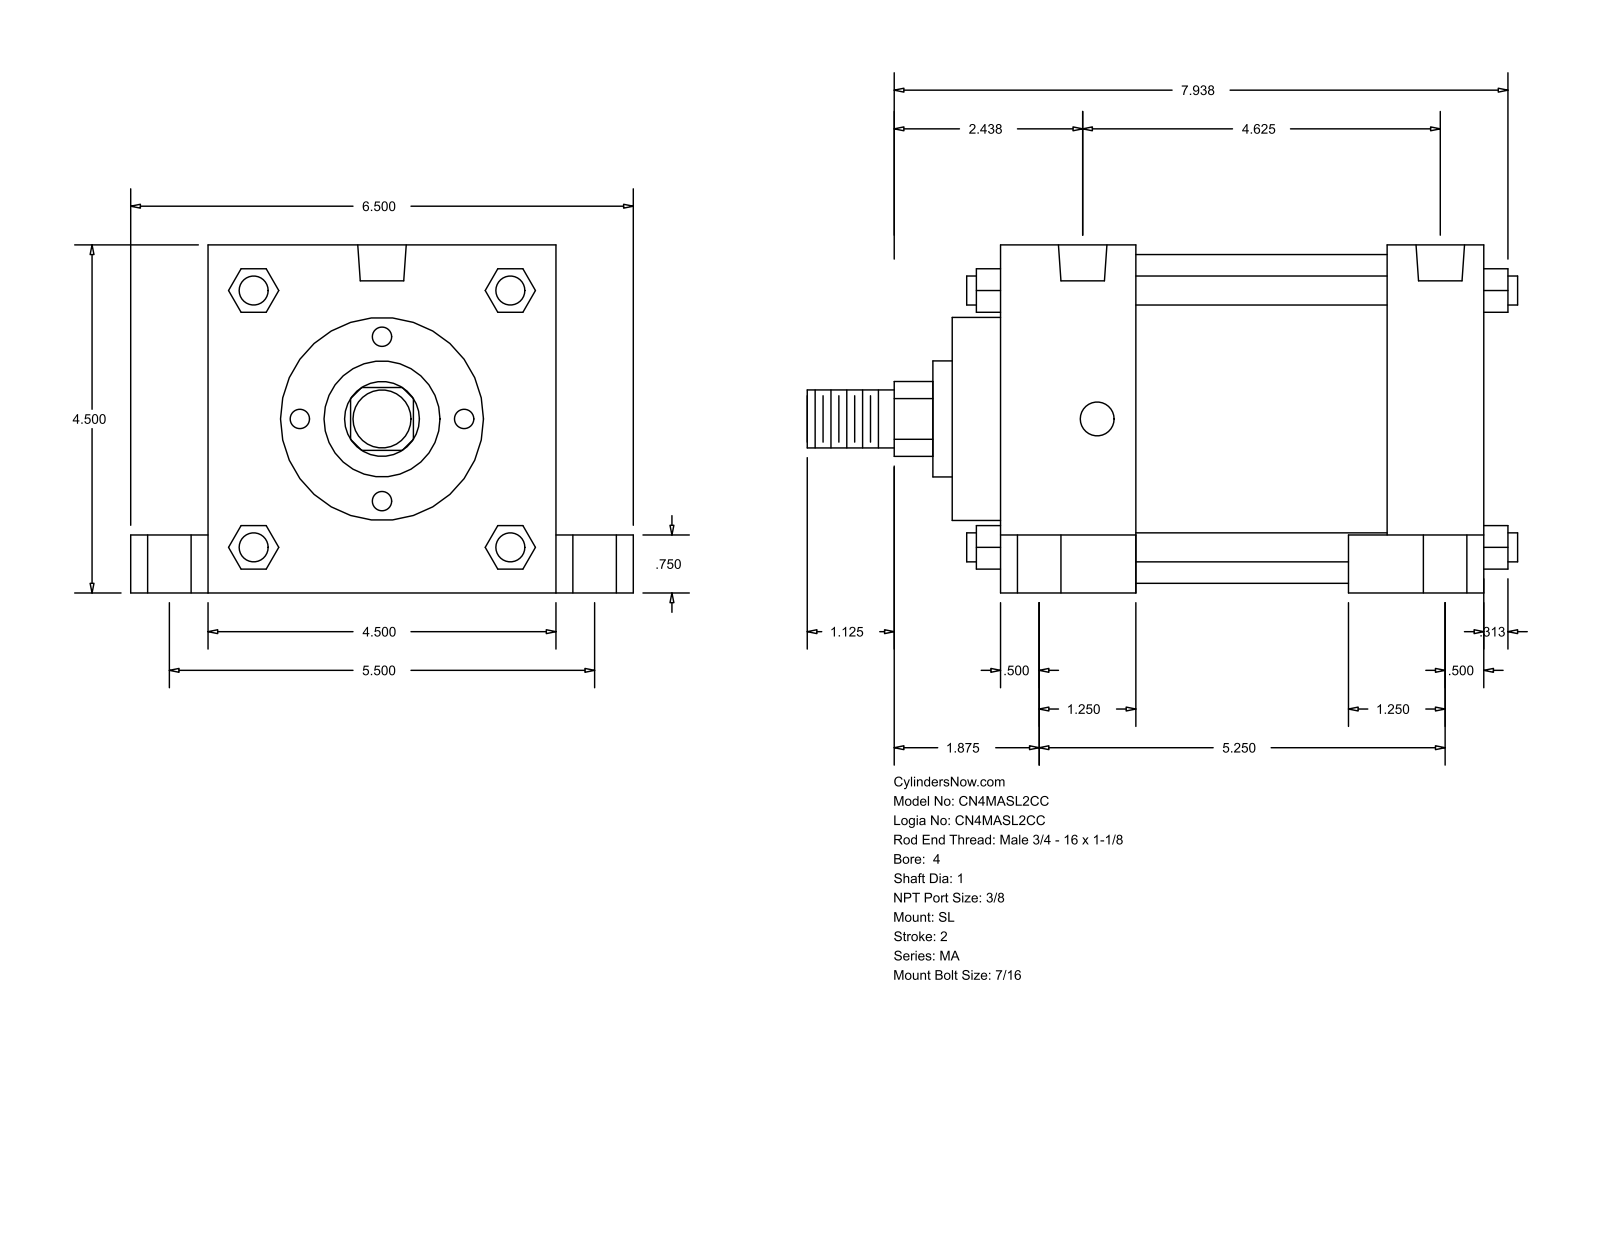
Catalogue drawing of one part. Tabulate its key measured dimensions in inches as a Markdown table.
| quantity | value |
| --- | --- |
| part name | MA_SL__0400_1 |
| STEP written by | GSSL Pune (CONFIG_CONTROL_DESIGN) |
| units | inches |
| bodies | 0 solids, 150 faces (113 planar, 37 cylindrical, 0 other) |
| overall size | 9.187 × 6.5 × 4.5 |
| round holes (diameter × count) | 0.437 × 4, 0.563 × 4, 0.813 × 4, 0.627 × 2 |
| round bosses / shafts (diameter × count) | 0.375 × 4, 4.25 × 1, 2.625 × 1, 1.5 × 1, 1 × 1, 0.75 × 1 |
| partial cylindrical surfaces (radius × count) | 0.484 × 1 |
| main face-to-face distances | 4.5, 6.25, 3.25, 1.75, 5, 1.25, 1, 5.5, 0.75, 3.75 |
| hole center spacings | 2.751, 2.761, 2.807, 2.85, 4.25, 5.25, 5.274, 5.435 |
